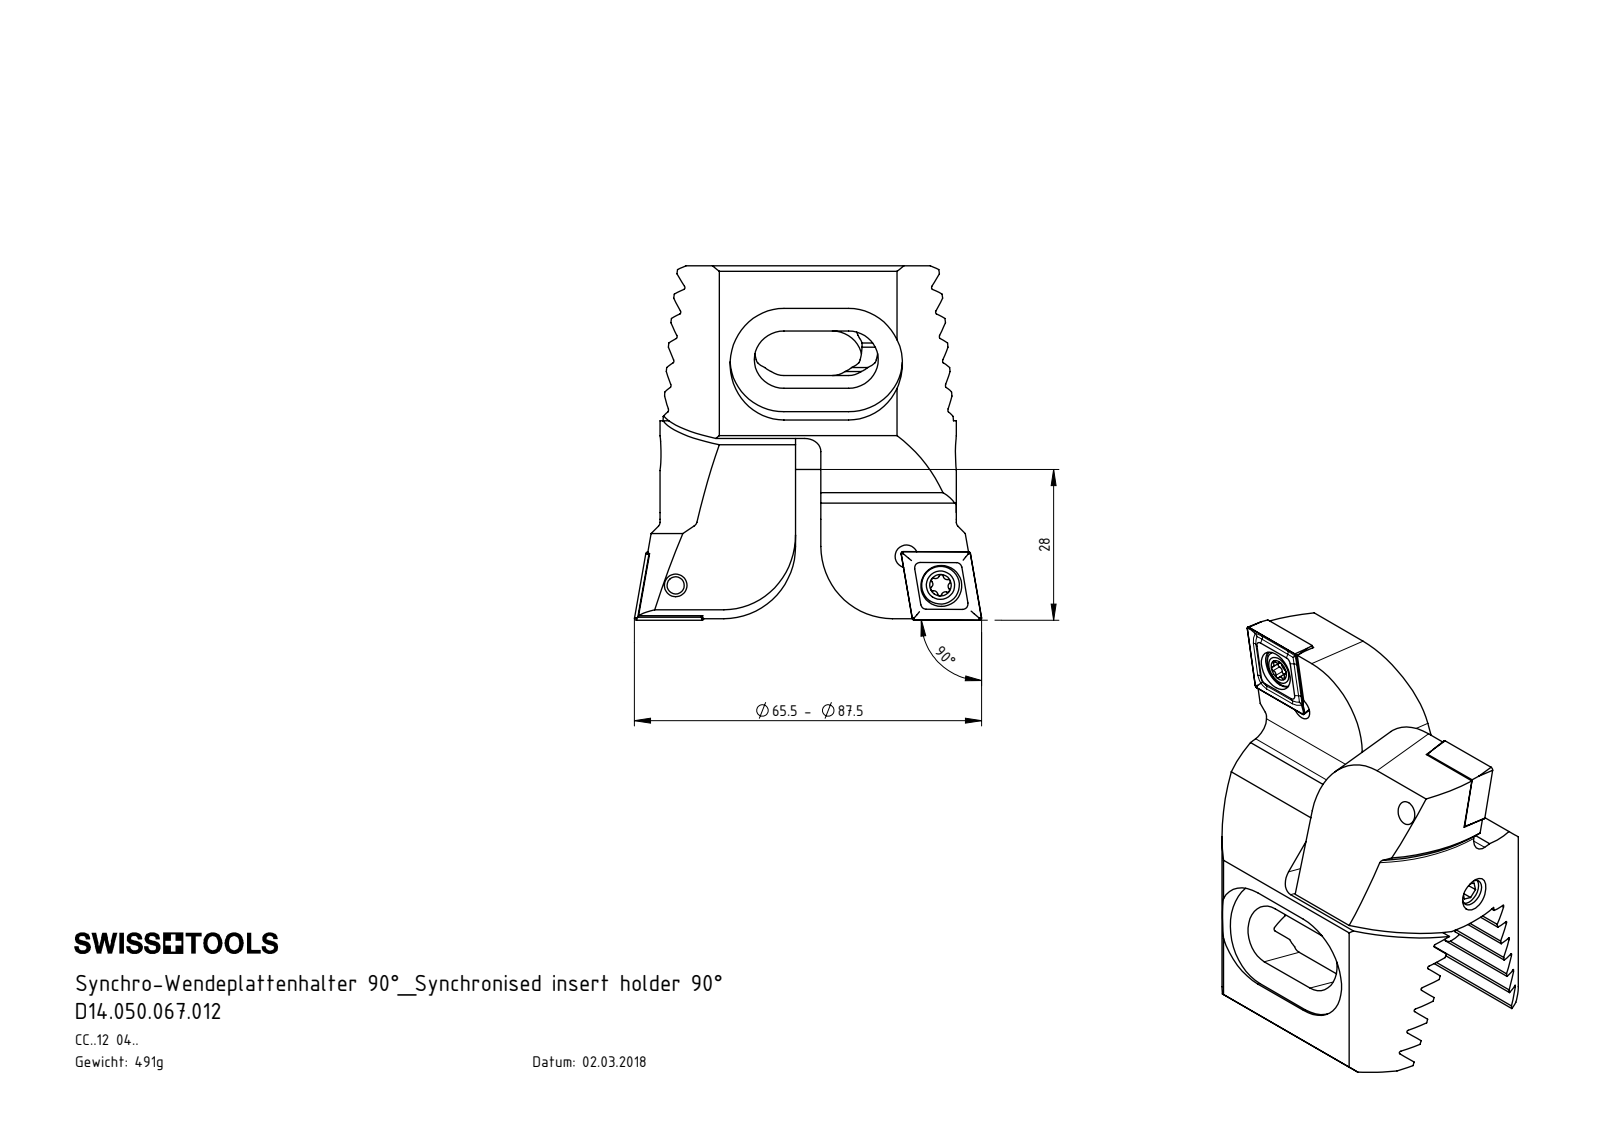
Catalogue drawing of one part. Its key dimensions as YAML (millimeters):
part_name: "Z55-WCC.B11.037; Z55-ER3.001.020; CCMT120404; WCC-ER2.001.010_A (+1 more)"
step_written_by: "SolidWorks 2012 (CONFIG_CONTROL_DESIGN)"
units: millimeters
bodies: {solids: 8, faces: 690, planar: 334, cylindrical: 132, other: 224}
overall_size: [65.8, 65.5, 44.2]
volume: 62094
surface_area: 22849
round_holes:
  - {diameter: 4.2, count: 4}
  - {diameter: 2, count: 2}
  - {diameter: 5.5, count: 2}
  - {diameter: 7.6, count: 2}
  - {diameter: 5, count: 1}
round_bosses_or_shafts:
  - {diameter: 7, count: 2}
  - {diameter: 5, count: 2}
  - {diameter: 6, count: 1}
  - {diameter: 4, count: 1}
partial_cylinders:
  - {radius: 1, count: 14}
  - {radius: 0.34, count: 12}
  - {radius: 0.39, count: 12}
  - {radius: 0.69, count: 12}
  - {radius: 3, count: 6}
  - {radius: 5.5, count: 4}
  - {radius: 9.25, count: 4}
  - {radius: 12, count: 4}
face_to_face_distances: [4.07, 8.14, 12.21, 16.28, 20.35, 7.85, 1.69, 21.8, 22.4, 5]
hole_center_spacings: [8.08, 8.2, 16, 44.46, 44.55, 50.43, 30.9, 37.96]
